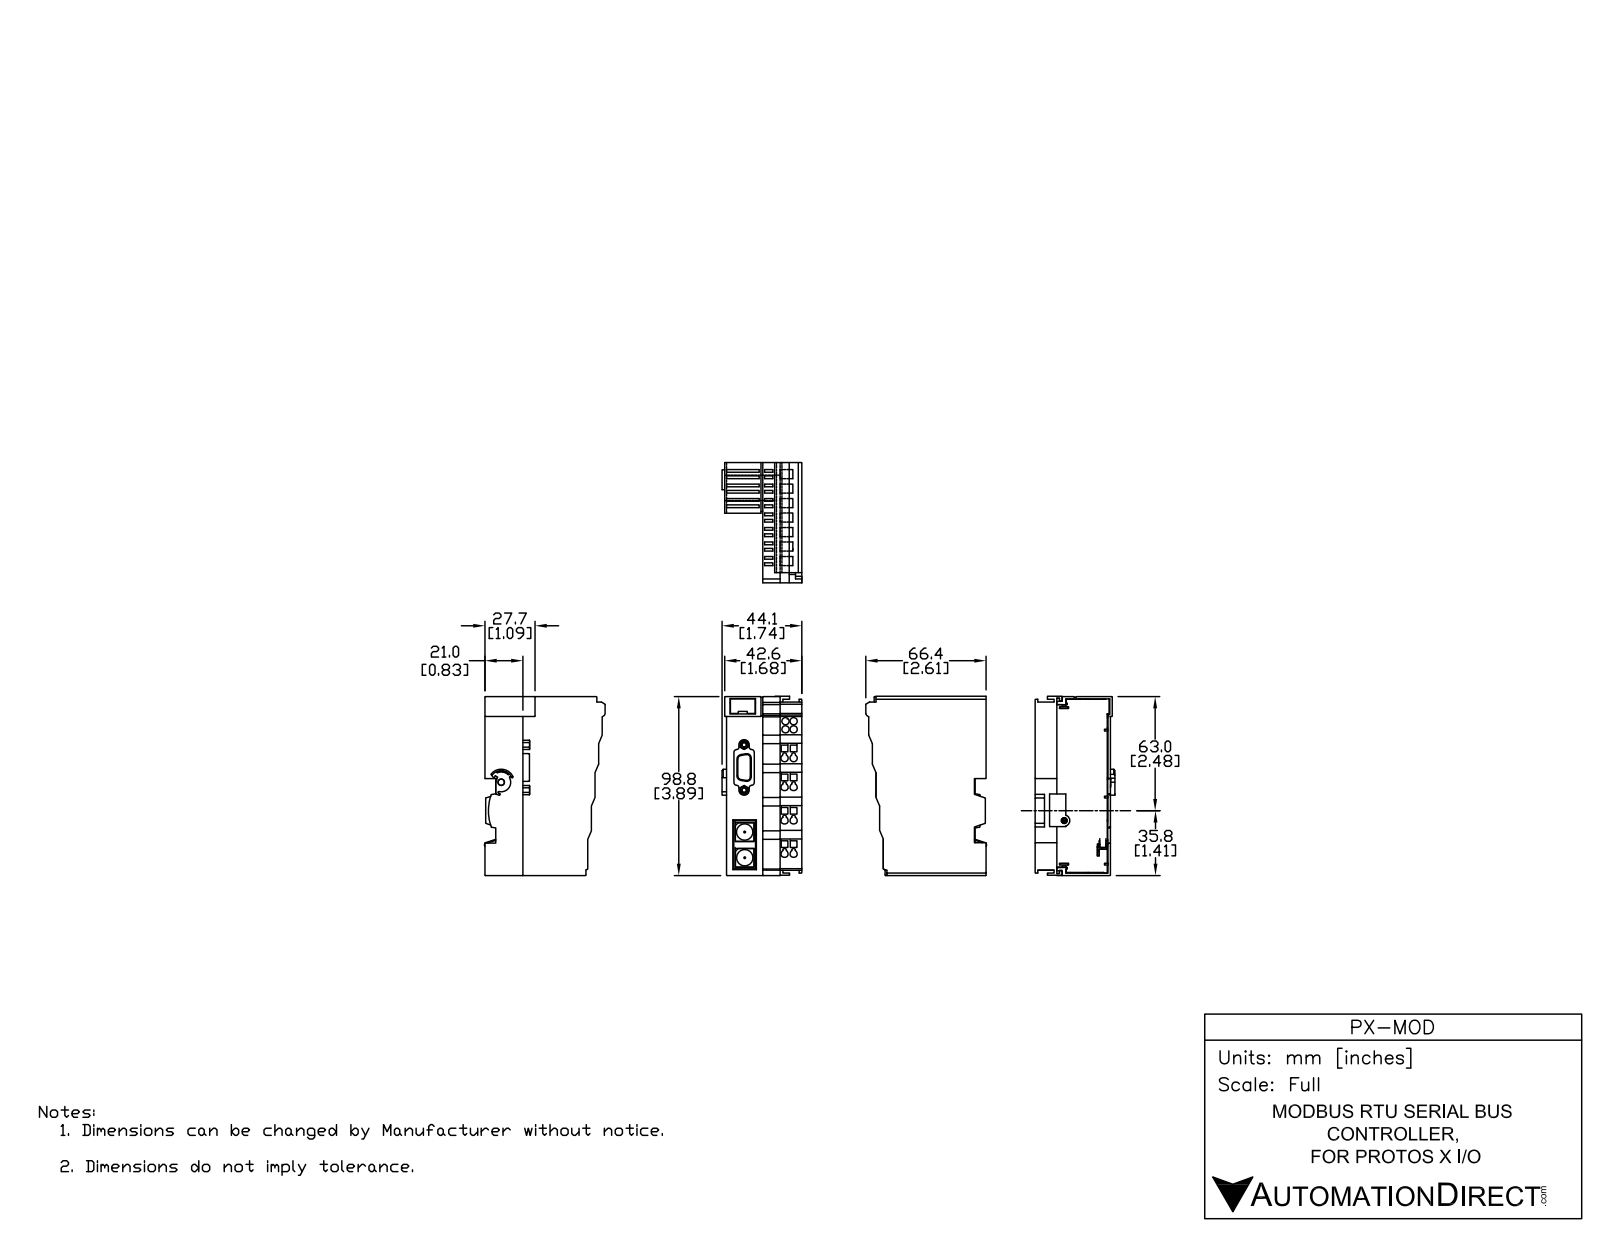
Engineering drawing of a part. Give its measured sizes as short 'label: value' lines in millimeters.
name: PX-MOD
written by: SolidWorks 2014 (AUTOMOTIVE_DESIGN)
unit: mm
bodies: 37 solids, 1979 faces (1446 planar, 457 cylindrical, 76 other)
size: 100.25 × 69.31 × 44.25
volume: 80 039 mm³; area: 72 459 mm²
holes: 10× ⌀4, 9× ⌀1, 2× ⌀2.4, 1× ⌀3.75
bosses: 2× ⌀10
rounds: 80× R0.25, 44× R0.3, 18× R0.4, 12× R0.38, 8× R1, 4× R0.1, 4× R0.17, 4× R1.03
face distances: 1, 8, 13, 20, 12, 21, 9, 7, 28, 29
hole spacings: 2.75, 5.5, 3.16, 3.26, 5, 18.4, 19.07, 4.95
